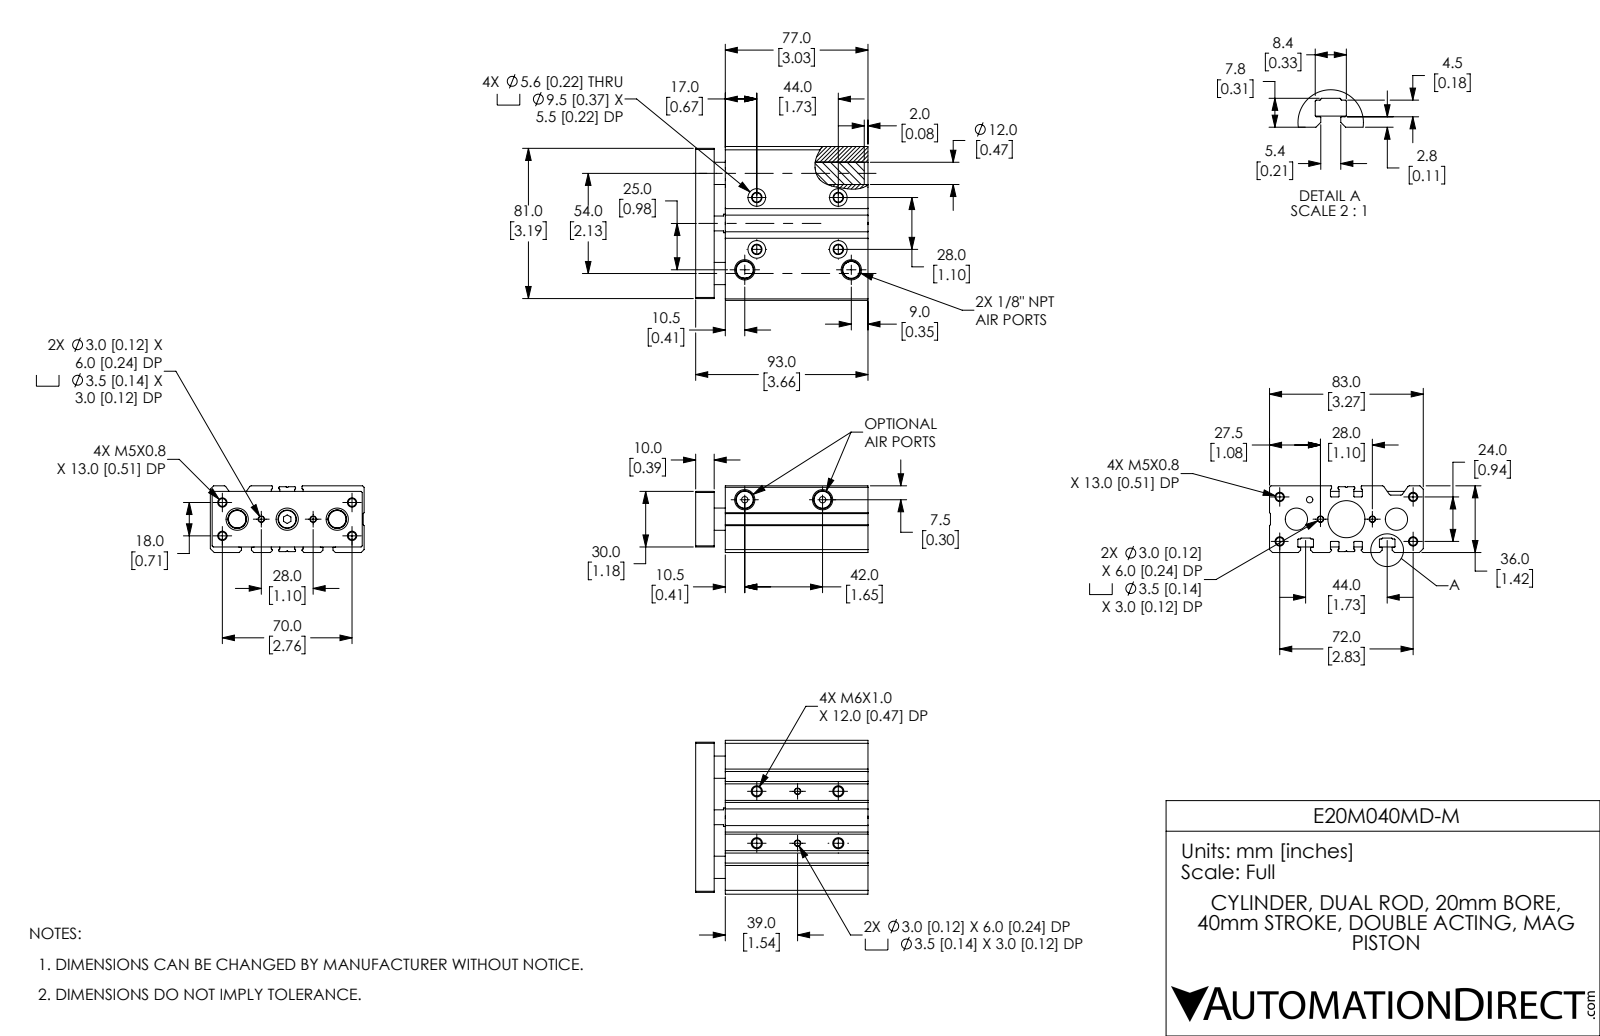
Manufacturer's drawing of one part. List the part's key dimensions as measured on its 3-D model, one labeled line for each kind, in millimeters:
Part name (STEP PRODUCT): E20M040MD-M_ENDPLATE; E20M040MD-M; E20M040MD-M_BODY
STEP written by: SolidWorks 2019 (CONFIG_CONTROL_DESIGN)
Units: millimetres
Bodies: 5 solids, 405 faces (128 planar, 182 cylindrical, 95 other)
Overall size (bounding box): 93 × 83 × 36
Volume: 214 221 mm³ · Surface area: 65 744 mm²
Round holes (diameter × count): ⌀4.13 ×8, ⌀3 ×4, ⌀3.5 ×4, ⌀4.92 ×4, ⌀5.6 ×4, ⌀9.5 ×4, ⌀6 ×3, ⌀12 ×3, ⌀3.43 ×2, ⌀9.91 ×2, ⌀3.43 ×1, ⌀12 ×1
Round bosses / shafts (diameter × count): ⌀10 ×1, ⌀9.91 ×1
Partial cylindrical surfaces — rounded edges, fillets, slot ends (radius × count): R0.4 ×20, R0.2 ×18, R0.3 ×10, R0.25 ×8, R1 ×4
Main face-to-face distances: 83, 36, 6, 3, 0.5, 16, 30, 93, 77, 10
Hole centre spacings: 3.16, 12.04, 15, 21.02, 22, 22.85, 25.06, 28
